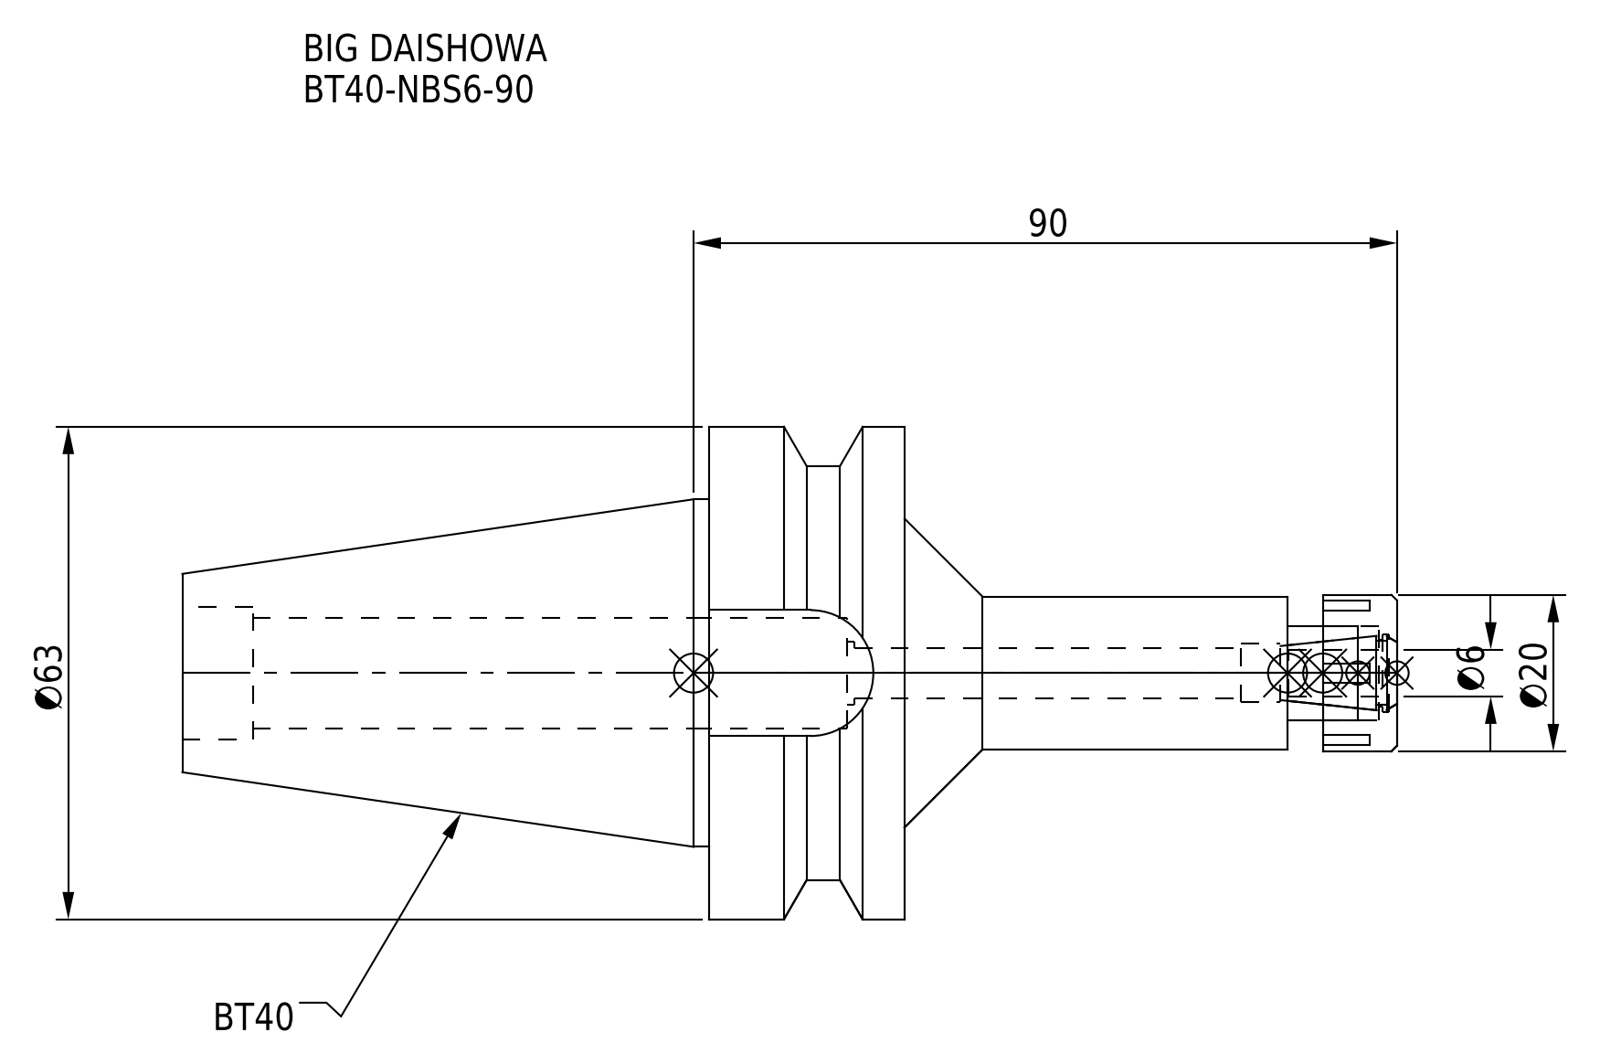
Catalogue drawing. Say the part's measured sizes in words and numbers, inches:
The part is named "DXF_TEMP_ASSY_ASM_4_ASM.stp; BT40-NBS6-90-FreeParts; BT40-NBS6-90_1.stp; BT40NB06090-060_ASM.stp (+3 more)". Its 3-D file was written by "SolidWorks 2019 (CONFIG_CONTROL_DESIGN)". It is 2 solids with 93 faces: 45 planar, 34 cylindrical and 14 other. Overall it measures 6.118 by 2.48 by 2.48 inches. Its volume is 8.512 cubic inches and its surface area 44.31 square inches. Round holes: 1 of diameter 0.252, 1 of diameter 0.295, 1 of diameter 0.315, 1 of diameter 0.335, 1 of diameter 0.394, 1 of diameter 0.472, 1 of diameter 0.559, 1 of diameter 0.669. Round bosses or shafts: 1 of diameter 2.48, 1 of diameter 2.087, 1 of diameter 1.75, 1 of diameter 0.787, 1 of diameter 0.768. Partial cylindrical surfaces (rounded edges, fillets, slot ends): 1 of radius 0.317. The main face-to-face distances are 0.984, 1.772, 3.638, 2.654, 5.567, 0.177, 2.48, 3.465, 6.118, 0.551.
